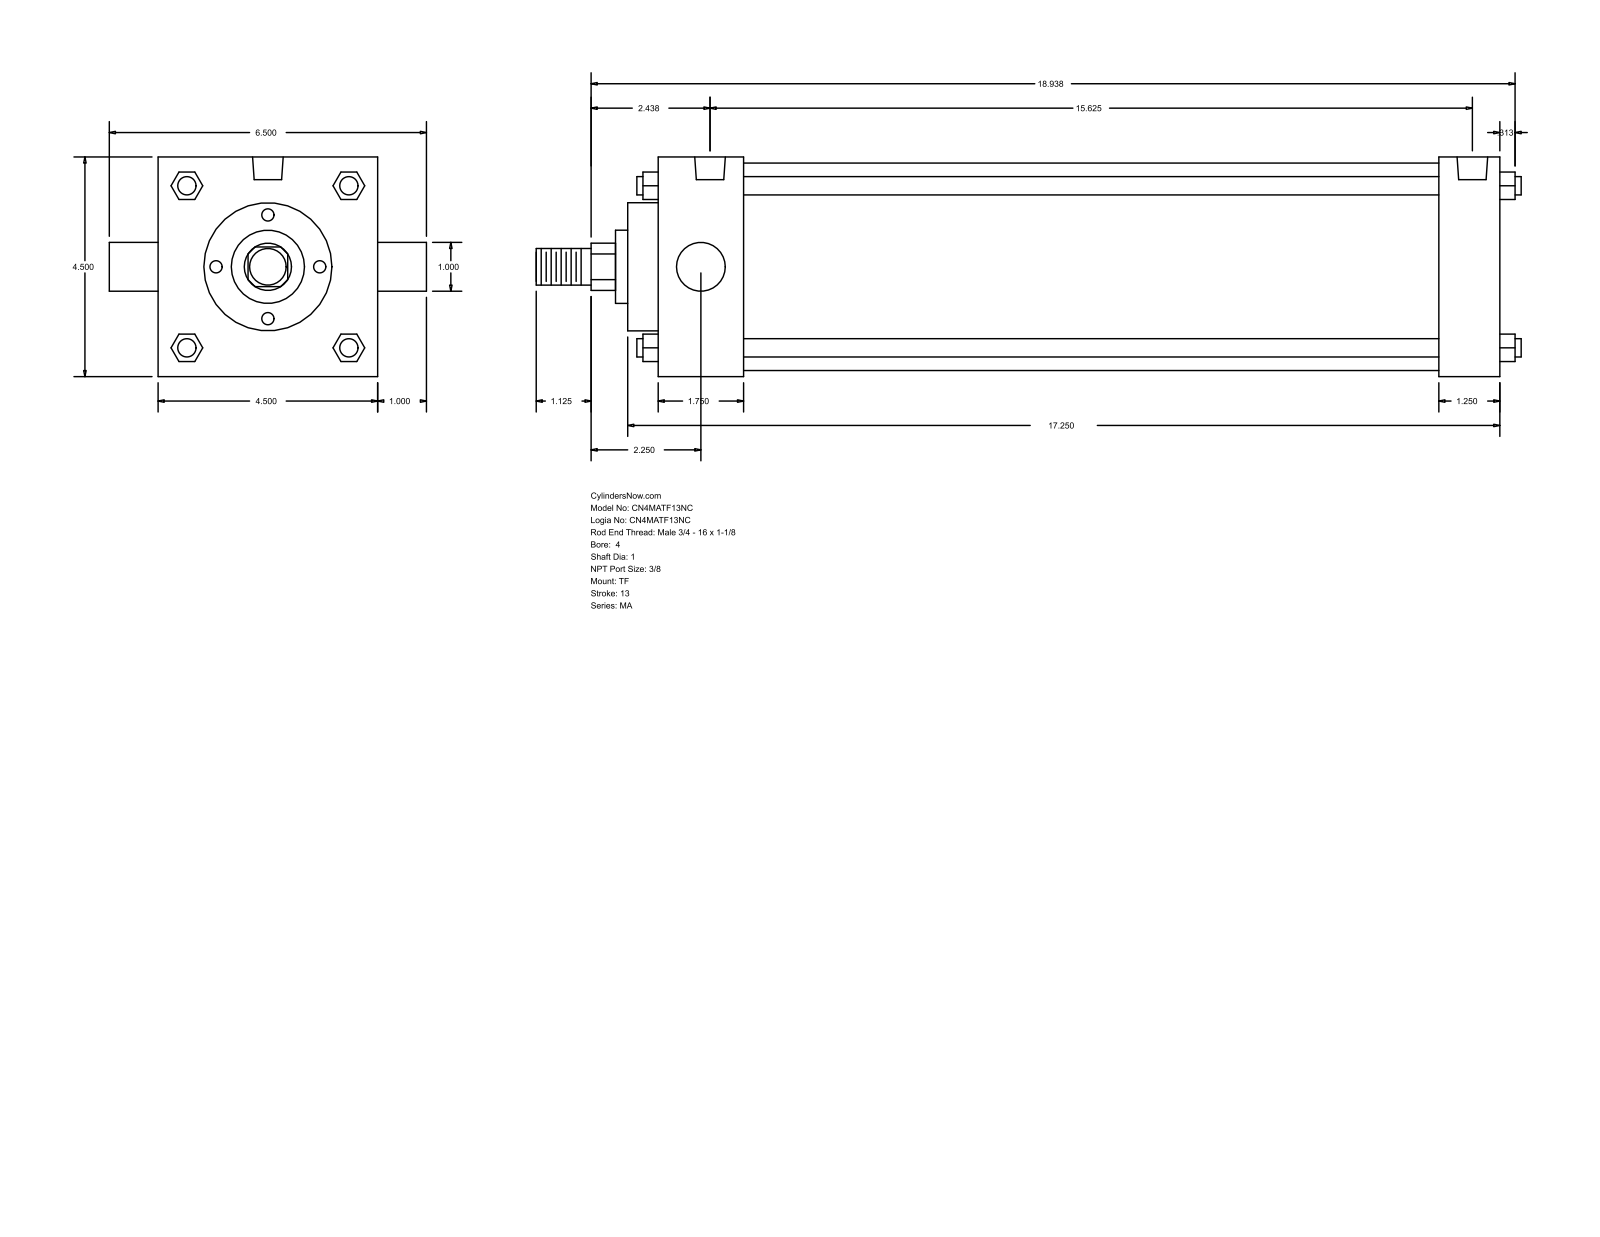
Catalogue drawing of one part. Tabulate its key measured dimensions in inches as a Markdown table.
| quantity | value |
| --- | --- |
| part name | MA_TF__0400_1 |
| STEP written by | GSSL Pune (CONFIG_CONTROL_DESIGN) |
| units | inches |
| bodies | 0 solids, 122 faces (93 planar, 29 cylindrical, 0 other) |
| overall size | 20.187 × 6.5 × 4.5 |
| round holes (diameter × count) | 0.437 × 3, 0.627 × 2 |
| round bosses / shafts (diameter × count) | 0.375 × 4, 1 × 2, 4.25 × 1, 2.625 × 1, 1.5 × 1, 0.75 × 1 |
| partial cylindrical surfaces (radius × count) | 0.484 × 1 |
| main face-to-face distances | 4.5, 17.25, 16, 1.25, 1.75, 14.25, 15.5, 17.875, 0.625, 2.375 |
| hole center spacings | 0.187, 0.188, 15.25, 15.437, 15.438, 15.625 |
